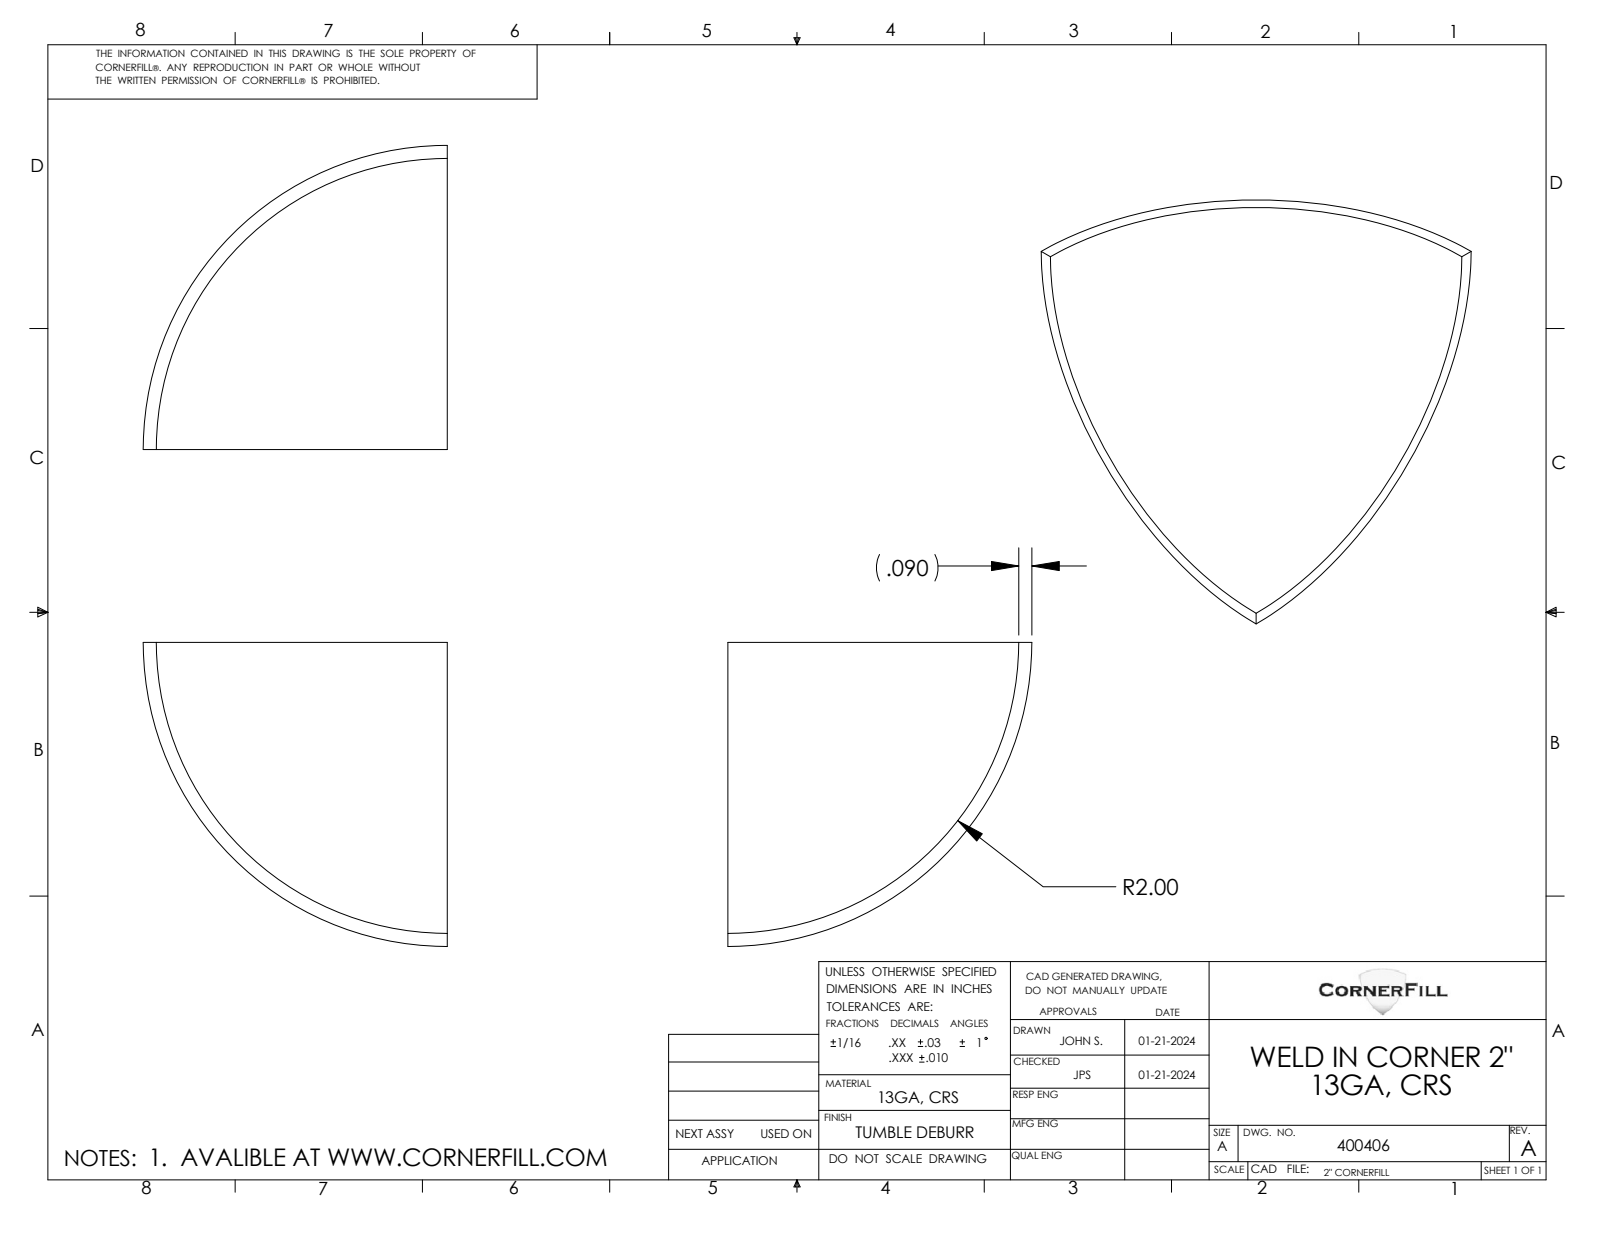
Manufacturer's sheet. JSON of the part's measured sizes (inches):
{"part_name": "400406", "step_written_by": "SolidWorks 2021 (CONFIG_CONTROL_DESIGN)", "units": "inches", "bodies": {"solids": 1, "faces": 5, "planar": 3, "cylindrical": 0, "other": 2}, "overall_size": [2.956, 2.09, 2.09], "volume_in3": 0.591, "surface_area_in2": 14.01}
